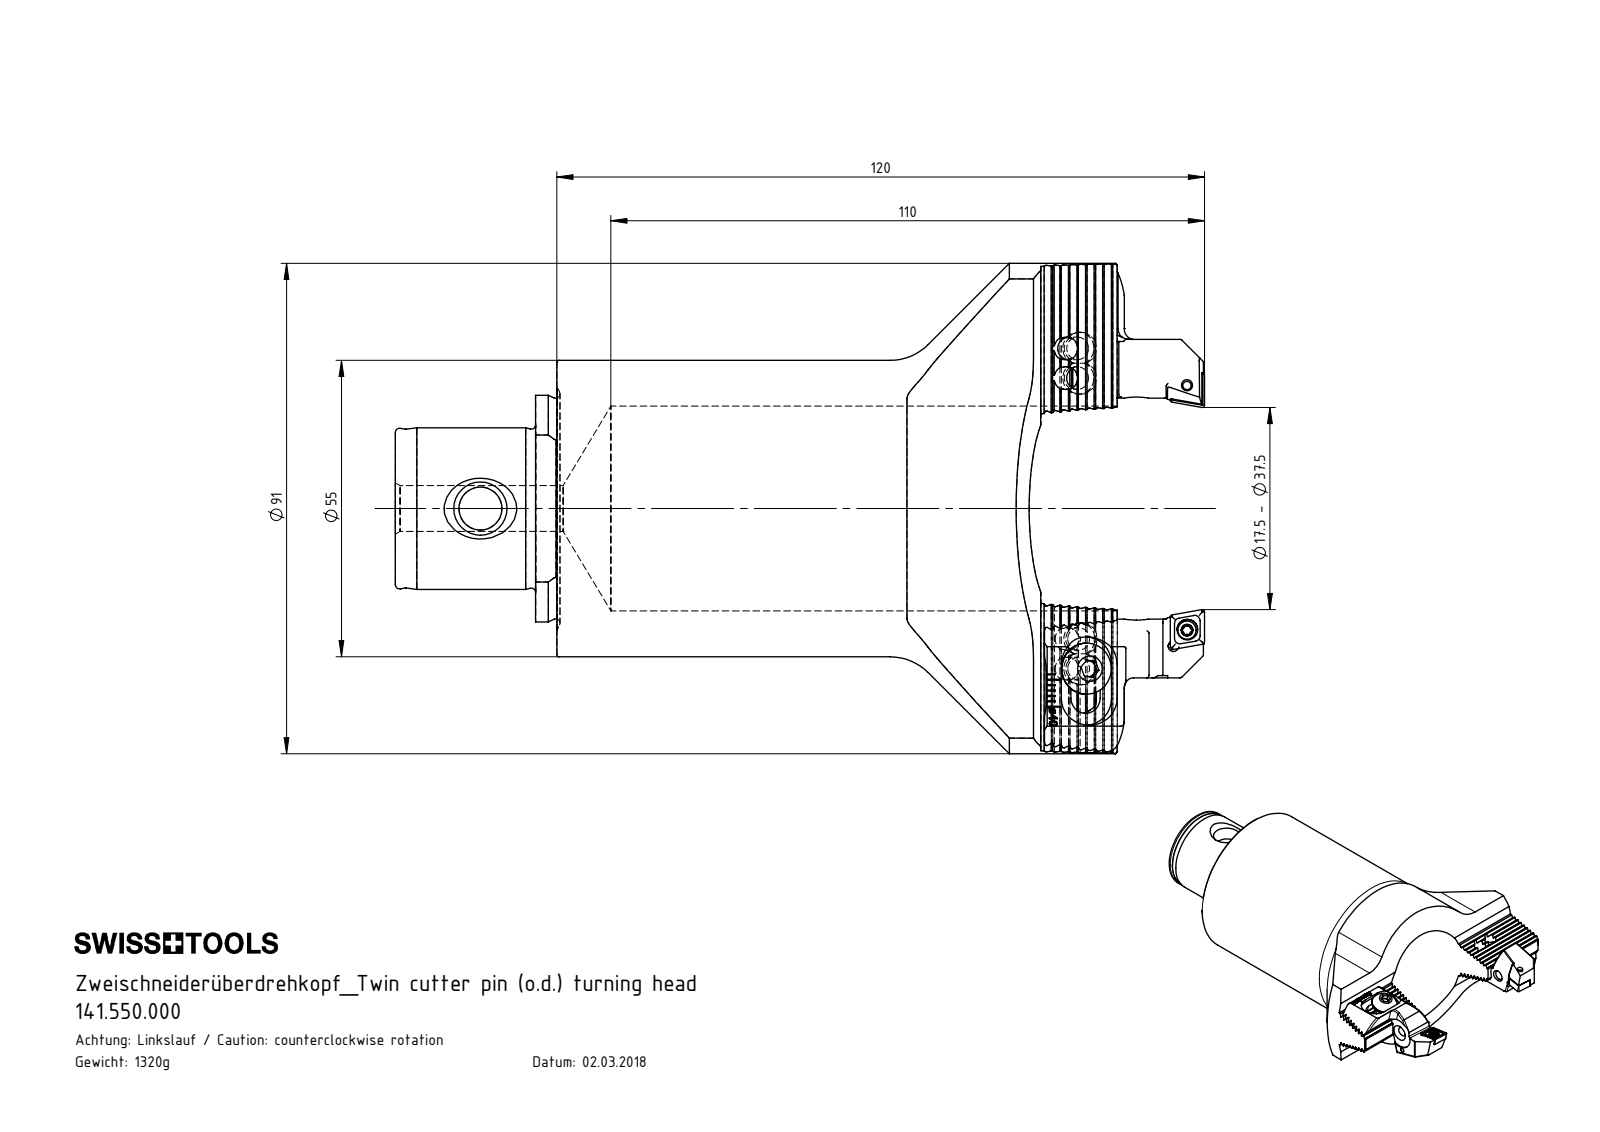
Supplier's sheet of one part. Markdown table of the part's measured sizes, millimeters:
| quantity | value |
| --- | --- |
| part name | CCMT060204; Z25-WCA.001.016_einzeln; 141.550.000; MB5-Z25.K05.120_C (+5 more) |
| STEP written by | SolidWorks 2017 (CONFIG_CONTROL_DESIGN) |
| units | millimeters |
| bodies | 11 solids, 1016 faces (521 planar, 248 cylindrical, 247 other) |
| overall size | 150.2 × 91 × 56 |
| volume | 168 673 mm³ |
| surface area | 44 656 mm² |
| round holes (diameter × count) | 4.2 × 4, 6 × 4, 1.6 × 2, 2 × 2, 2.05 × 2, 2.8 × 2, 3.5 × 2, 3.85 × 2, 5.3 × 2, 8 × 1, 8.5 × 1, 38 × 1 |
| round bosses / shafts (diameter × count) | 9.5 × 2, 9.2 × 2, 5 × 2, 3.4 × 2, 2.5 × 2, 55 × 1, 30 × 1 |
| partial cylindrical surfaces (radius × count) | 0.12 × 18, 0.5 × 18, 0.12 × 16, 0.21 × 12, 0.36 × 10, 2 × 4, 2.8 × 4, 5 × 4 |
| main face-to-face distances | 1.43, 2.86, 7.14, 5.71, 8.57, 4.28, 30, 4.29, 3.95, 2.85 |
| hole center spacings | 3.9, 4, 5.5, 7, 7.11, 44.94, 47.99, 48.07 |
